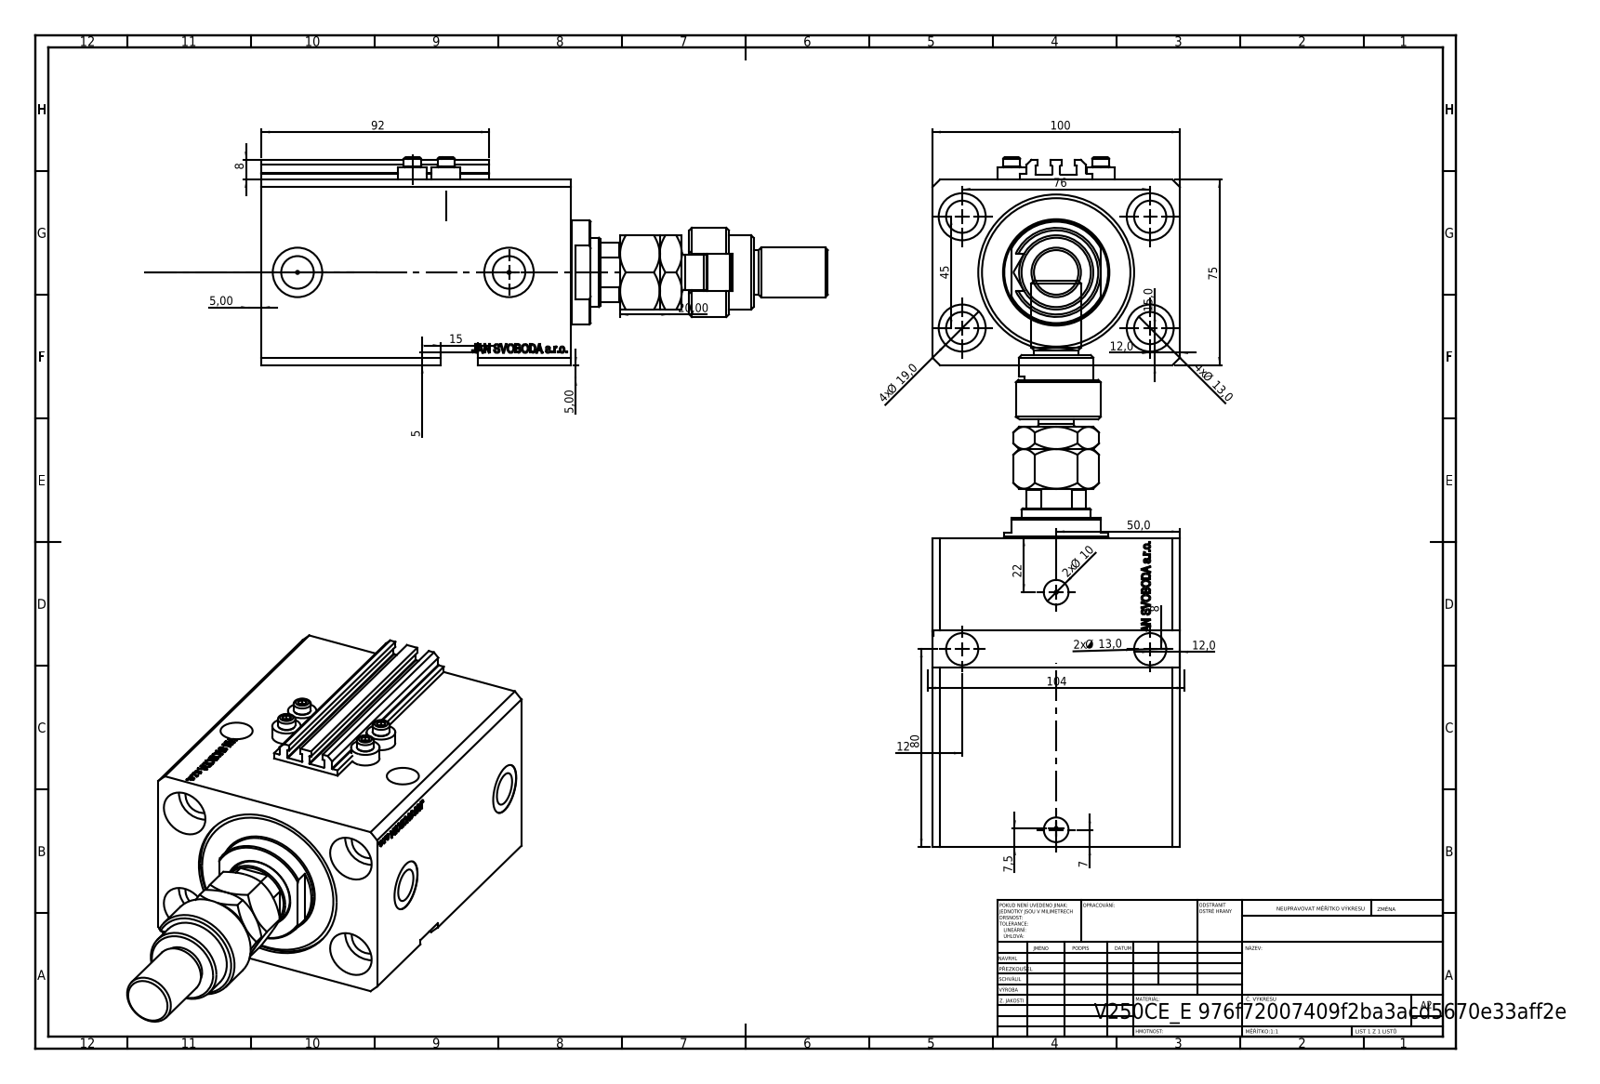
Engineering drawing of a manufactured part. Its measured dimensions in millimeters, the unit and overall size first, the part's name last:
Units: millimetres
Overall size (bounding box): 228.9 × 100 × 84
Round holes (diameter × count): ⌀13 ×6, ⌀1.25 ×4, ⌀4 ×4, ⌀19 ×4, ⌀10 ×2, ⌀13.16 ×2, ⌀20 ×2, ⌀18.5 ×1, ⌀28 ×1, ⌀50 ×1, ⌀63 ×1
Round bosses / shafts (diameter × count): ⌀11.6 ×4, ⌀7 ×4, ⌀42 ×1, ⌀36 ×1, ⌀30 ×1, ⌀22 ×1, ⌀20 ×1, ⌀18 ×1
Partial cylindrical surfaces — rounded edges, fillets, slot ends (radius × count): R0.2 ×10, R7.5 ×1, R12 ×1, R13.5 ×1
Main face-to-face distances: 75, 100, 125, 11.9, 113.1, 98.4, 86.5, 26.6, 30, 48.4
Hole centre spacings: 44.16, 76, 13.6, 20.72, 27.59, 33.62, 36, 38.48
Volume: 828 116 mm³ · Surface area: 163 492 mm²
Bodies: 10 solids, 1189 faces (567 planar, 151 cylindrical, 471 other)
Part name (STEP PRODUCT): V250CE_VC_E; V250CE_E; MFA; V250CE_C_VCP (+2 more)
STEP written by: SolidWorks 2019 (CONFIG_CONTROL_DESIGN)
